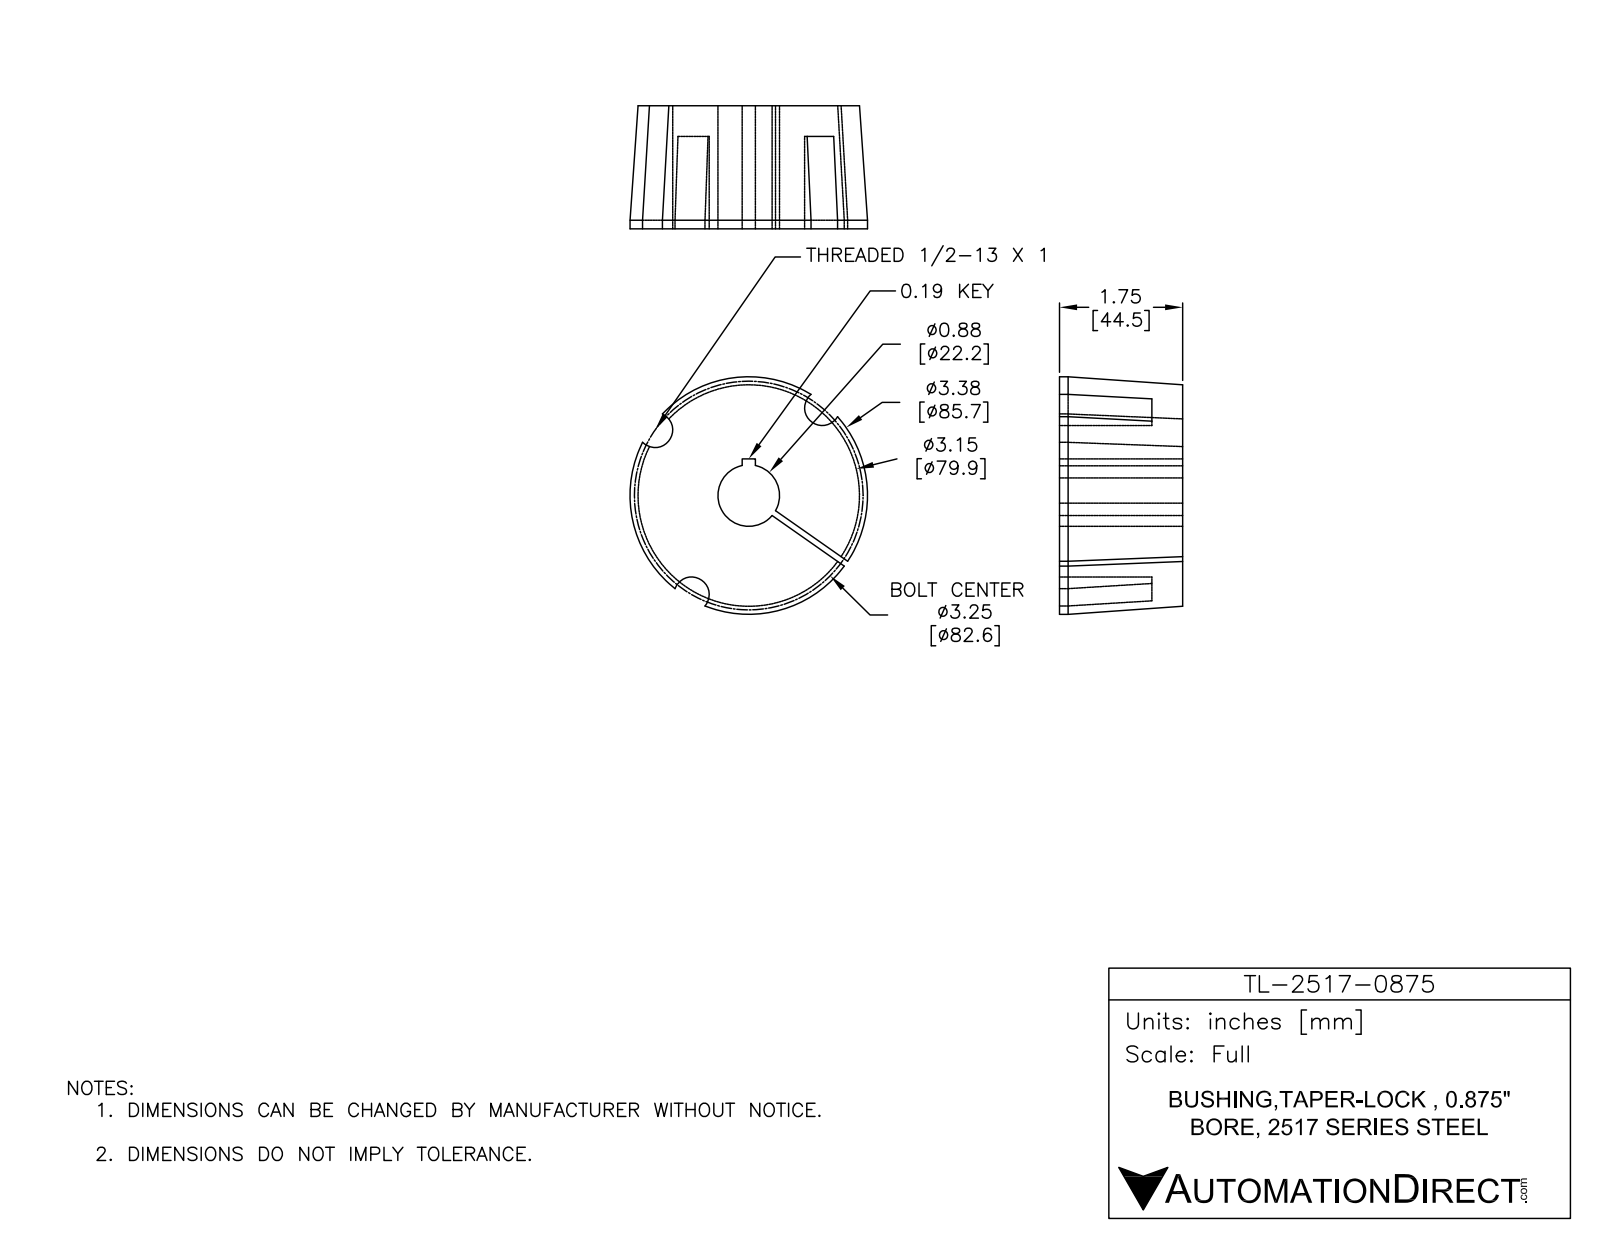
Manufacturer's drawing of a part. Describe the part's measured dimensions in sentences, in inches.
The part is named "TL-2517-0875". Its 3-D file was written by "SolidWorks 2014 (AUTOMOTIVE_DESIGN)". It is 1 solid with 25 faces: 9 planar, 13 cylindrical and 3 other. Overall it measures 3.375 by 3.375 by 1.75 inches. Its volume is 12.98 cubic inches and its surface area 43.29 square inches. Round holes: 1 of diameter 0.875. Round bosses or shafts: 1 of diameter 3.375. Partial cylindrical surfaces (rounded edges, fillets, slot ends): 3 of radius 0.25. The main face-to-face distances are 1.75, 0.085, 0.437, 1.313, 0.187.
